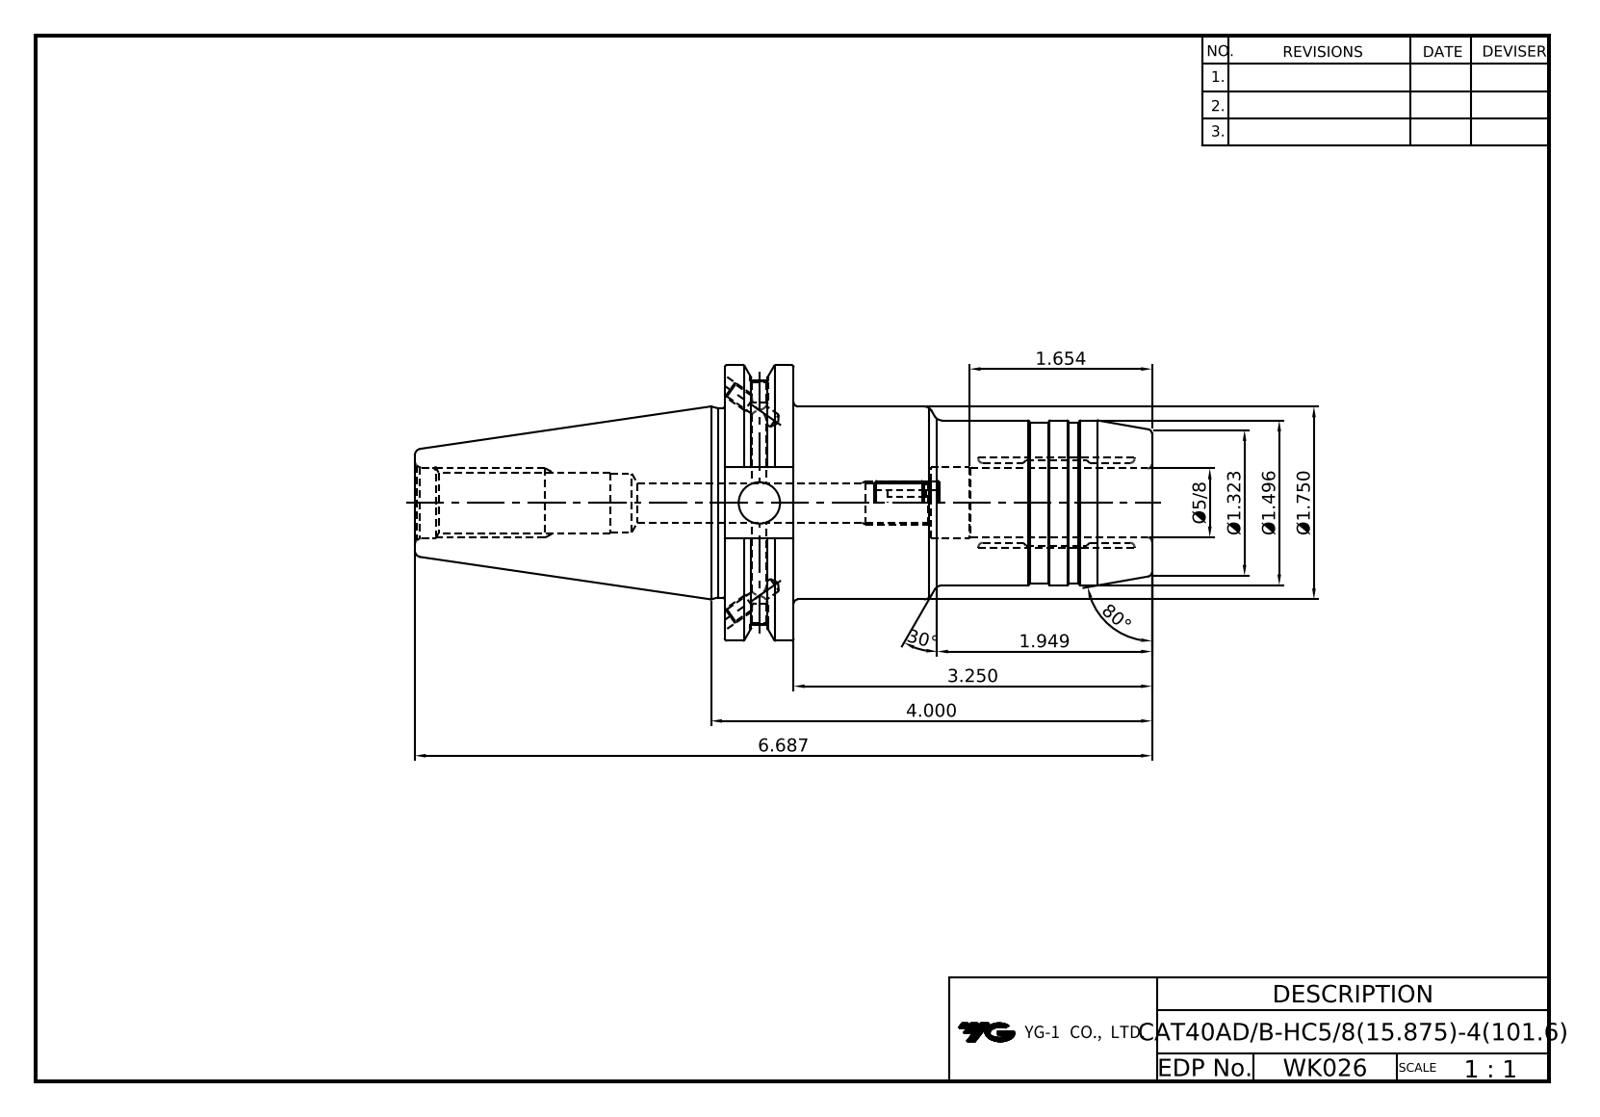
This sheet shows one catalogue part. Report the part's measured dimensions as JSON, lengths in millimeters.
{"part_name": "LO-CAT40ADB-HC15.875-101.6", "step_written_by": "Autodesk Inventor 2020 (AUTOMOTIVE_DESIGN)", "units": "millimeters", "bodies": {"solids": 1, "faces": 108, "planar": 37, "cylindrical": 34, "other": 37}, "overall_size": [169.85, 63.5, 61.09], "volume_mm3": 196309, "surface_area_mm2": 33743, "round_holes": [[3.24, 4], [4, 2], [4.2, 2], [8.92, 1], [9.53, 1], [13, 1], [13.39, 1], [15.88, 1], [16.3, 1], [16.4, 1]], "round_bosses_or_shafts": [[63.5, 1], [44.45, 1], [43.6, 1], [38, 1], [37, 1]], "partial_cylinders_radius": [[28.15, 1]], "face_to_face_distances": [15.88, 98.43, 82.55, 47.6, 16.38, 47.43, 31.55, 51, 71.42, 87.3]}
